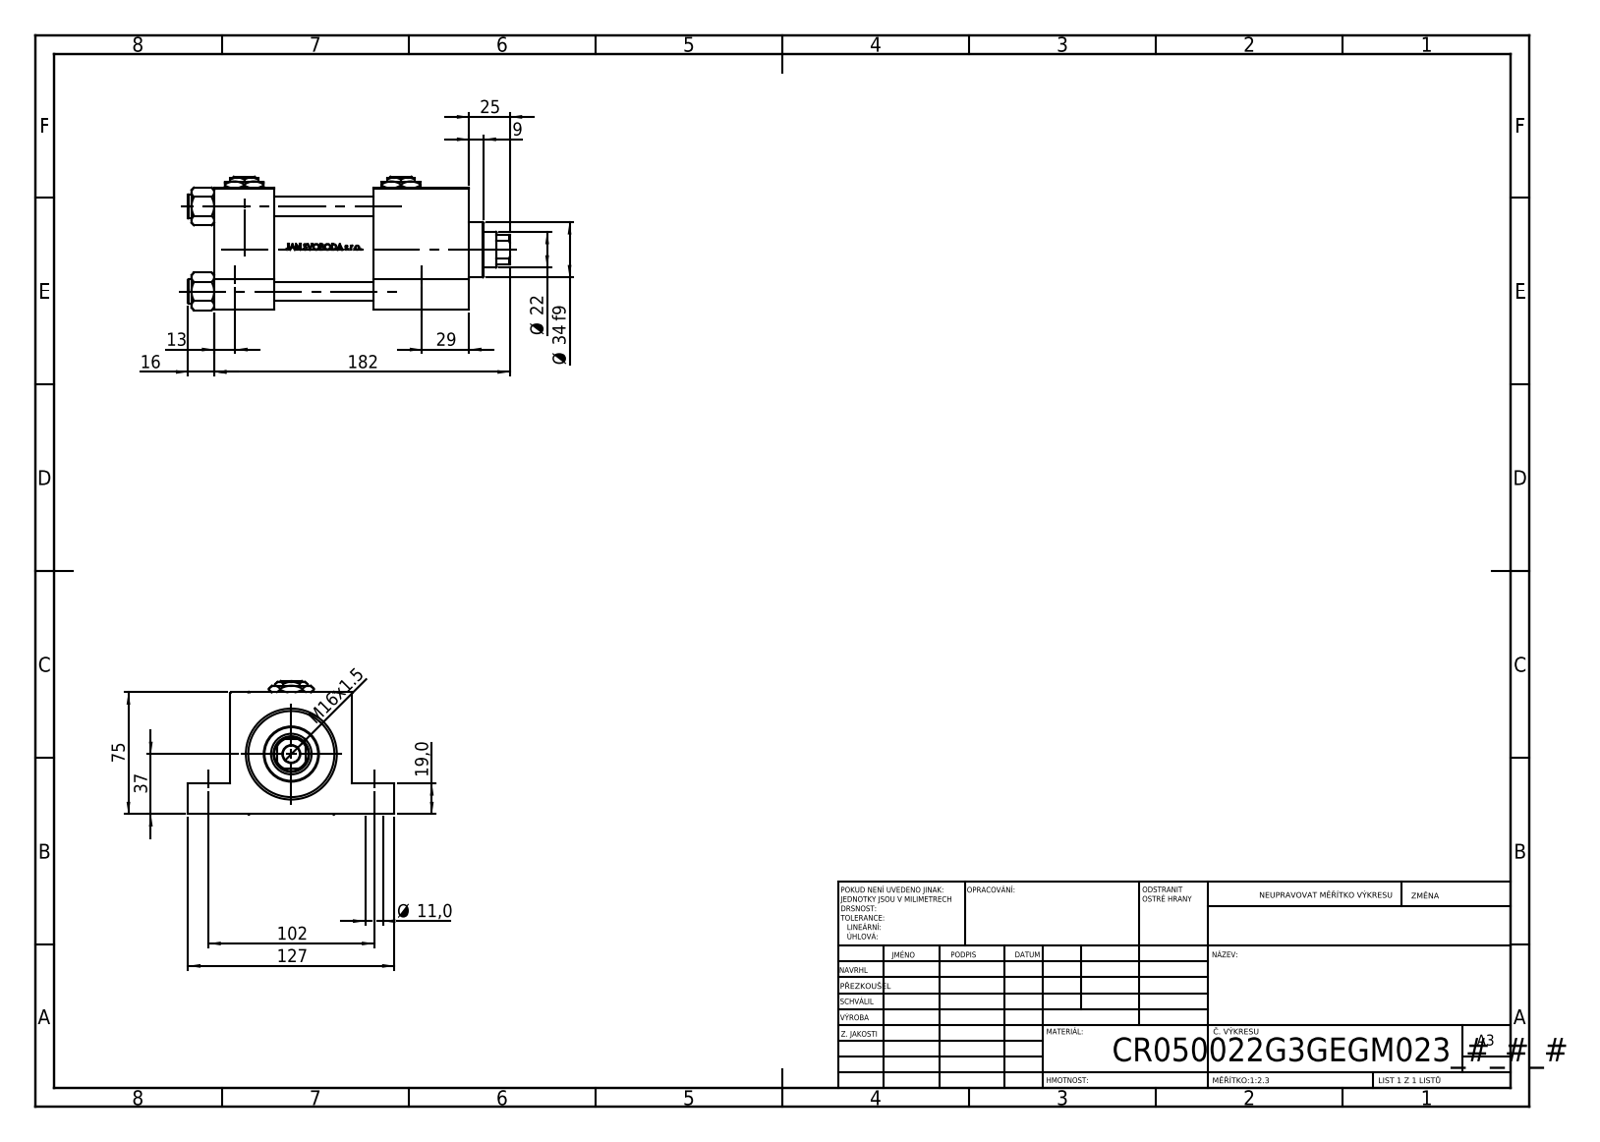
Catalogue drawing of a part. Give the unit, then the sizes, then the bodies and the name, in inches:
Units: inches
Overall size (bounding box): 7.795 × 5 × 3.239
Round holes (diameter × count): ⌀0.433 ×4, ⌀0.472 ×4, ⌀0.276 ×2, ⌀0.825 ×2, ⌀1.181 ×2, ⌀0.413 ×1, ⌀0.866 ×1, ⌀0.984 ×1, ⌀1.614 ×1, ⌀1.969 ×1, ⌀2.087 ×1
Round bosses / shafts (diameter × count): ⌀0.591 ×4, ⌀2.205 ×1, ⌀1.339 ×1
Partial cylindrical surfaces — rounded edges, fillets, slot ends (radius × count): R0.413 ×1
Main face-to-face distances: 2.953, 1.457, 6.181, 4.724, 0.748, 2.205, 3.858, 2.402, 2.323, 1.024
Hole centre spacings: 2.059, 1.442, 1.47, 2.02, 2.072, 2.912, 4.016, 4.49
Volume: 46.7 in³ · Surface area: 254.1 in²
Bodies: 13 solids, 1172 faces (476 planar, 124 cylindrical, 572 other)
Part name (STEP PRODUCT): NUT_M5_G; V215CR_G_Body; Zatka_pro_OIL_PORT; V215CR_VCP_G (+2 more)
STEP written by: SolidWorks 2019 (CONFIG_CONTROL_DESIGN)
